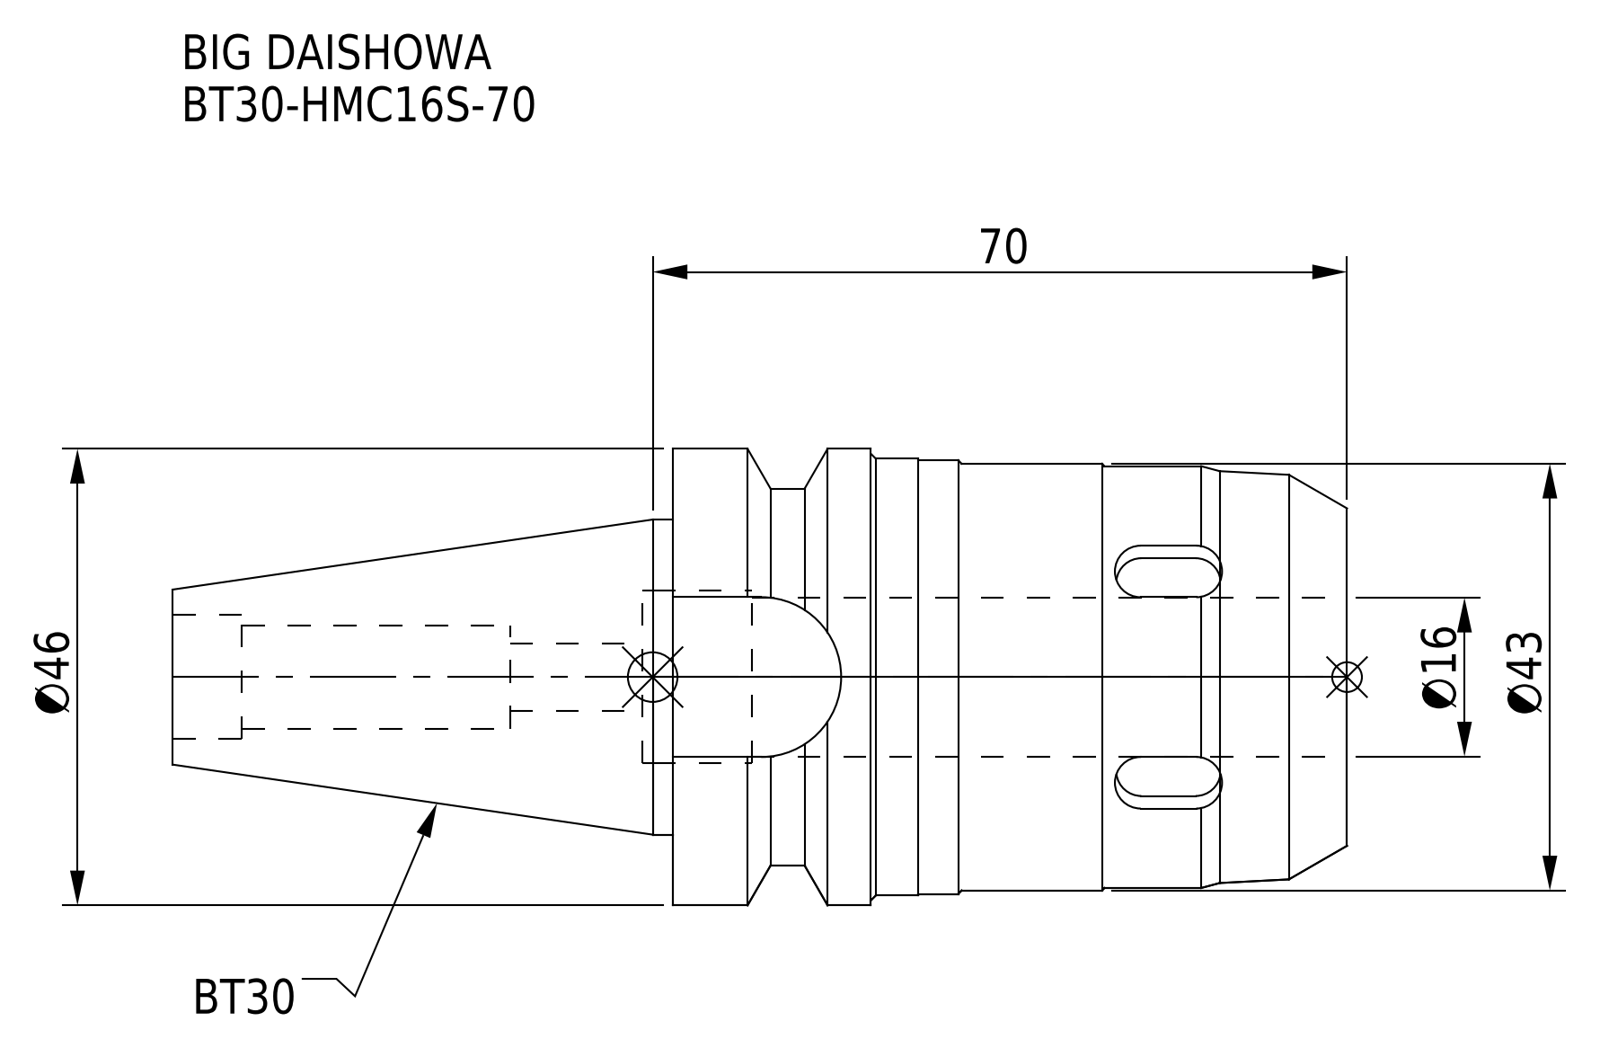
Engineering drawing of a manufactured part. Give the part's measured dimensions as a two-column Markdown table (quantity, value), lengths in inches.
| quantity | value |
| --- | --- |
| part name | BT30-HMC16S-70 |
| STEP written by | CREO PARAMETRIC BY PTC INC, 2016380 (AUTOMOTIVE_DESIGN) |
| units | inches |
| bodies | 1 solid, 97 faces (33 planar, 42 cylindrical, 22 other) |
| overall size | 4.661 × 1.811 × 1.811 |
| volume | 6.162 in³ |
| surface area | 33.21 in² |
| round holes (diameter × count) | 0.268 × 1, 0.409 × 1, 0.492 × 1, 0.63 × 1, 0.685 × 1 |
| round bosses / shafts (diameter × count) | 1.811 × 1, 1.732 × 1, 1.72 × 1, 1.693 × 1, 1.673 × 1, 1.25 × 1 |
| partial cylindrical surfaces (radius × count) | 0.118 × 6, 0.317 × 1, 0.748 × 1 |
| main face-to-face distances | 2.677, 1.283, 2.795, 0.118, 1.496, 4.661, 1.984, 1.866, 0.431, 1.065 |
